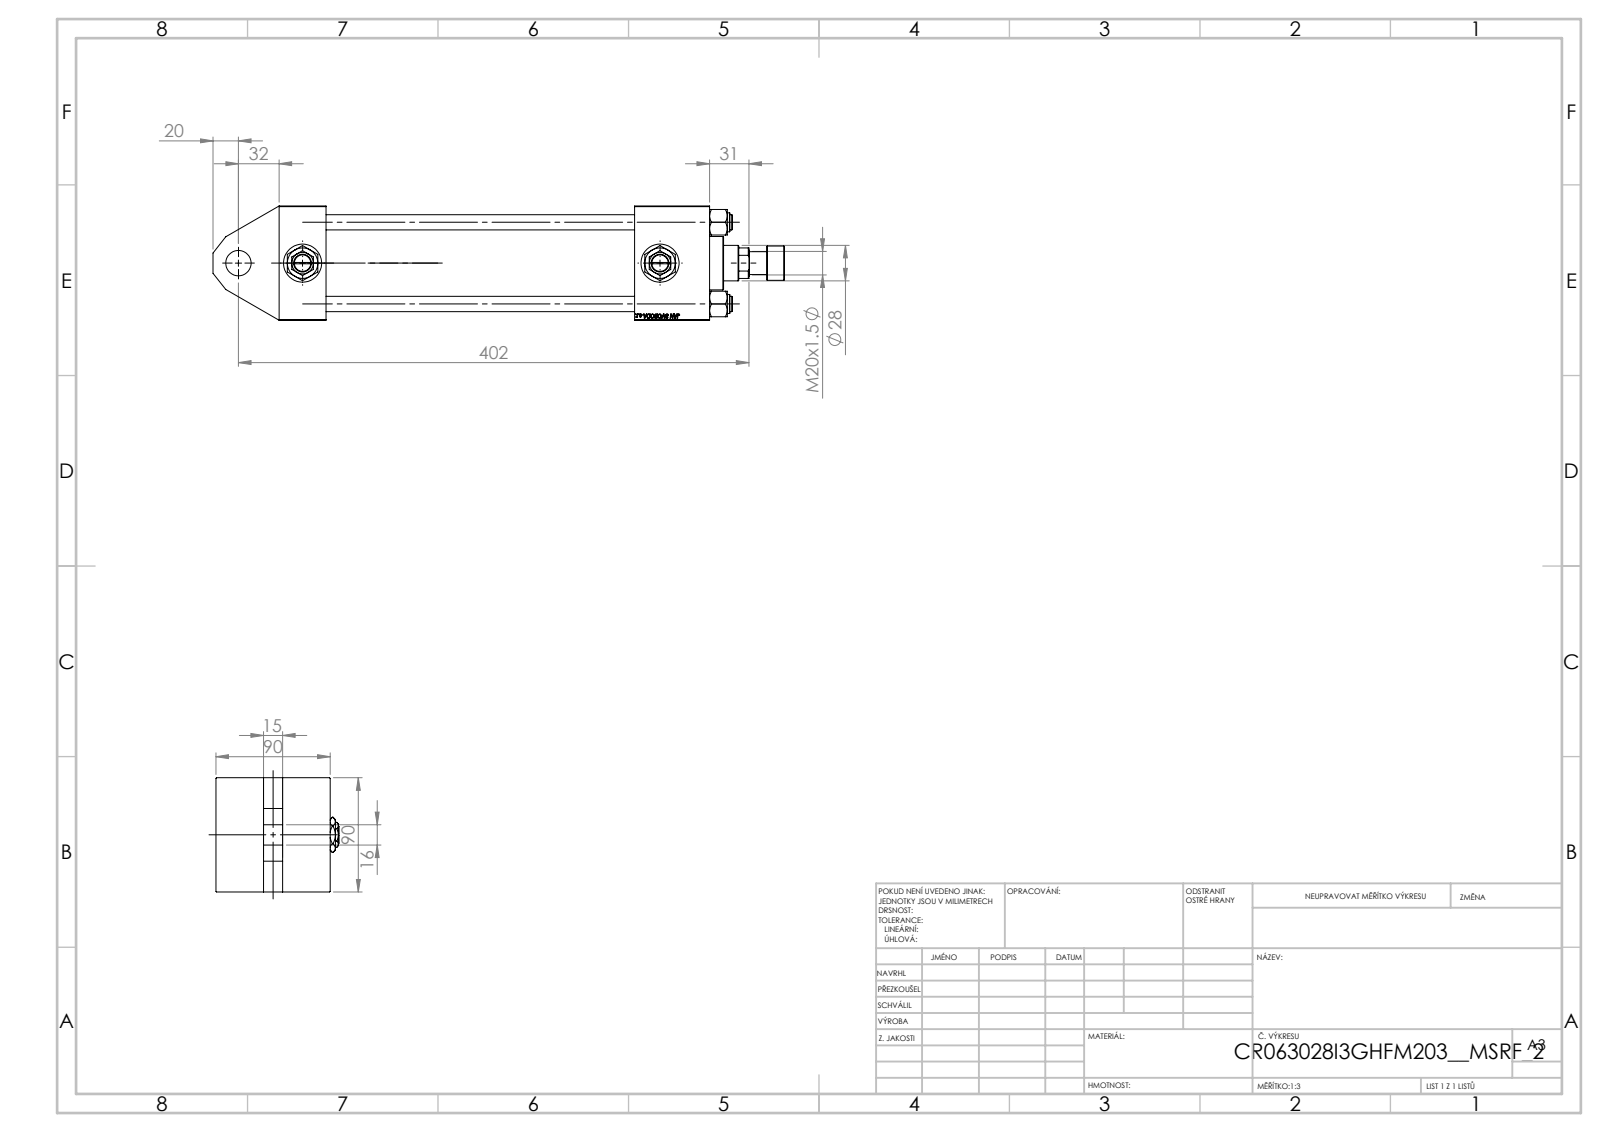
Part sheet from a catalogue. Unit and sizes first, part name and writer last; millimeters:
Units: millimetres
Overall size (bounding box): 450 × 97 × 90
Round holes (diameter × count): ⌀12 ×4, ⌀7 ×2, ⌀20.96 ×2, ⌀30 ×2, ⌀18.5 ×1, ⌀20 ×1, ⌀28 ×1, ⌀31 ×1, ⌀50 ×1, ⌀60 ×1, ⌀63 ×1
Round bosses / shafts (diameter × count): ⌀15 ×4, ⌀69 ×1, ⌀42 ×1, ⌀27 ×1, ⌀18 ×1
Main face-to-face distances: 90, 37, 339, 302, 59, 37.5, 52.5, 280, 243, 310.3
Hole centre spacings: 45.47, 64.3, 90.93, 50.5, 281.5, 332
Volume: 1 315 000 mm³ · Surface area: 317 773 mm²
Bodies: 14 solids, 1194 faces (554 planar, 96 cylindrical, 544 other)
Part name (STEP PRODUCT): V215CR_TYCINKA_I; NUT_M5_I; V215CR_I_Body; V215_VC_A (+3 more)
STEP written by: SolidWorks 2019 (CONFIG_CONTROL_DESIGN)
